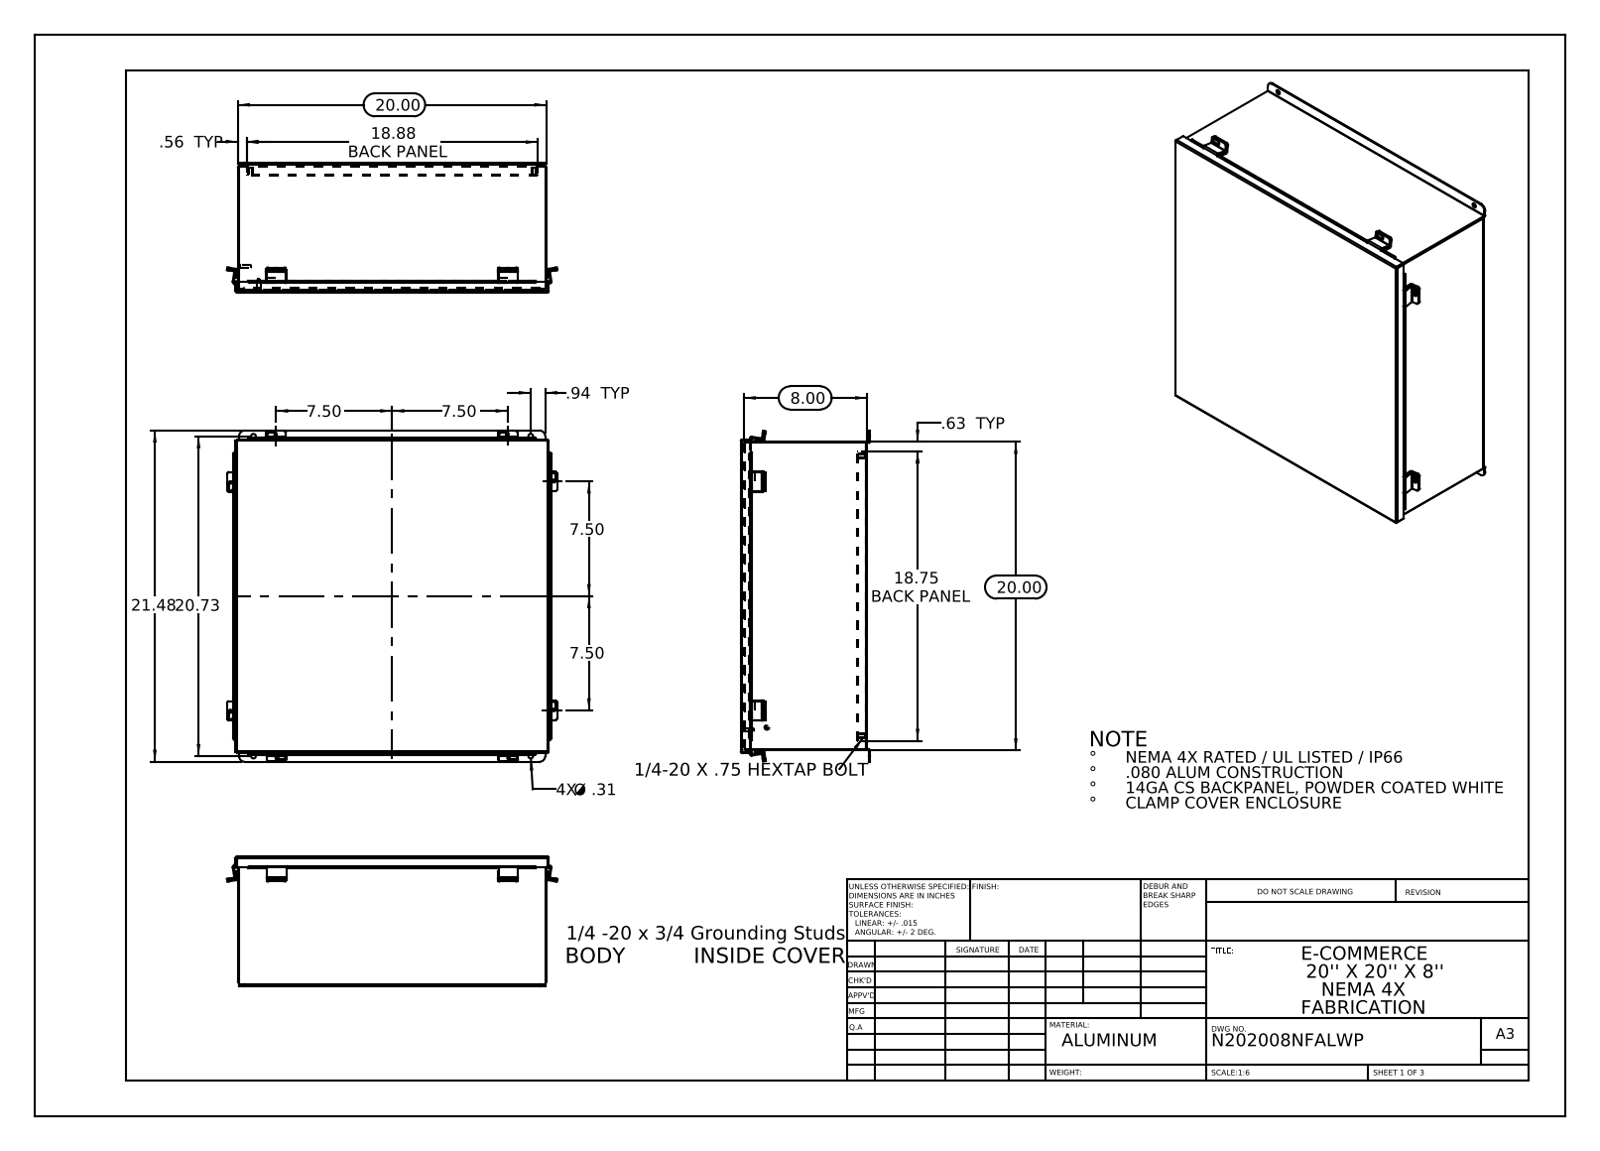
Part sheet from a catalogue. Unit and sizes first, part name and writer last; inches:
Units: inches
Overall size (bounding box): 21.476 × 21.407 × 8.39
Round holes (diameter × count): ⌀0.25 ×12, ⌀0.187 ×4, ⌀0.312 ×4
Round bosses / shafts (diameter × count): ⌀0.313 ×4, ⌀0.315 ×2, ⌀0.236 ×2
Partial cylindrical surfaces — rounded edges, fillets, slot ends (radius × count): R0.125 ×32, R0.009 ×16, R0.133 ×16, R0.013 ×12, R0.088 ×12, R0.083 ×8, R0.1 ×8, R0.084 ×4
Main face-to-face distances: 0.075, 8.128, 19.925, 8.053, 8.203, 7.628, 0.575, 0.5, 7.553, 0.649
Hole centre spacings: 1.315, 18.222, 19.427, 26.603, 14.85, 15, 17.976, 18.126
Volume: 145.1 in³ · Surface area: 3 916 in²
Bodies: 27 solids, 640 faces (420 planar, 200 cylindrical, 20 other)
Part name (STEP PRODUCT): N202008NFSSWP JIC Clamp Bracket; N202008NFSSWP JIC_Standoff; N202008NFSSWP HW-CD-S-25020-034; N202008NFSSWP JIC Backpanel (+6 more)
STEP written by: SolidWorks 2013 (CONFIG_CONTROL_DESIGN)
